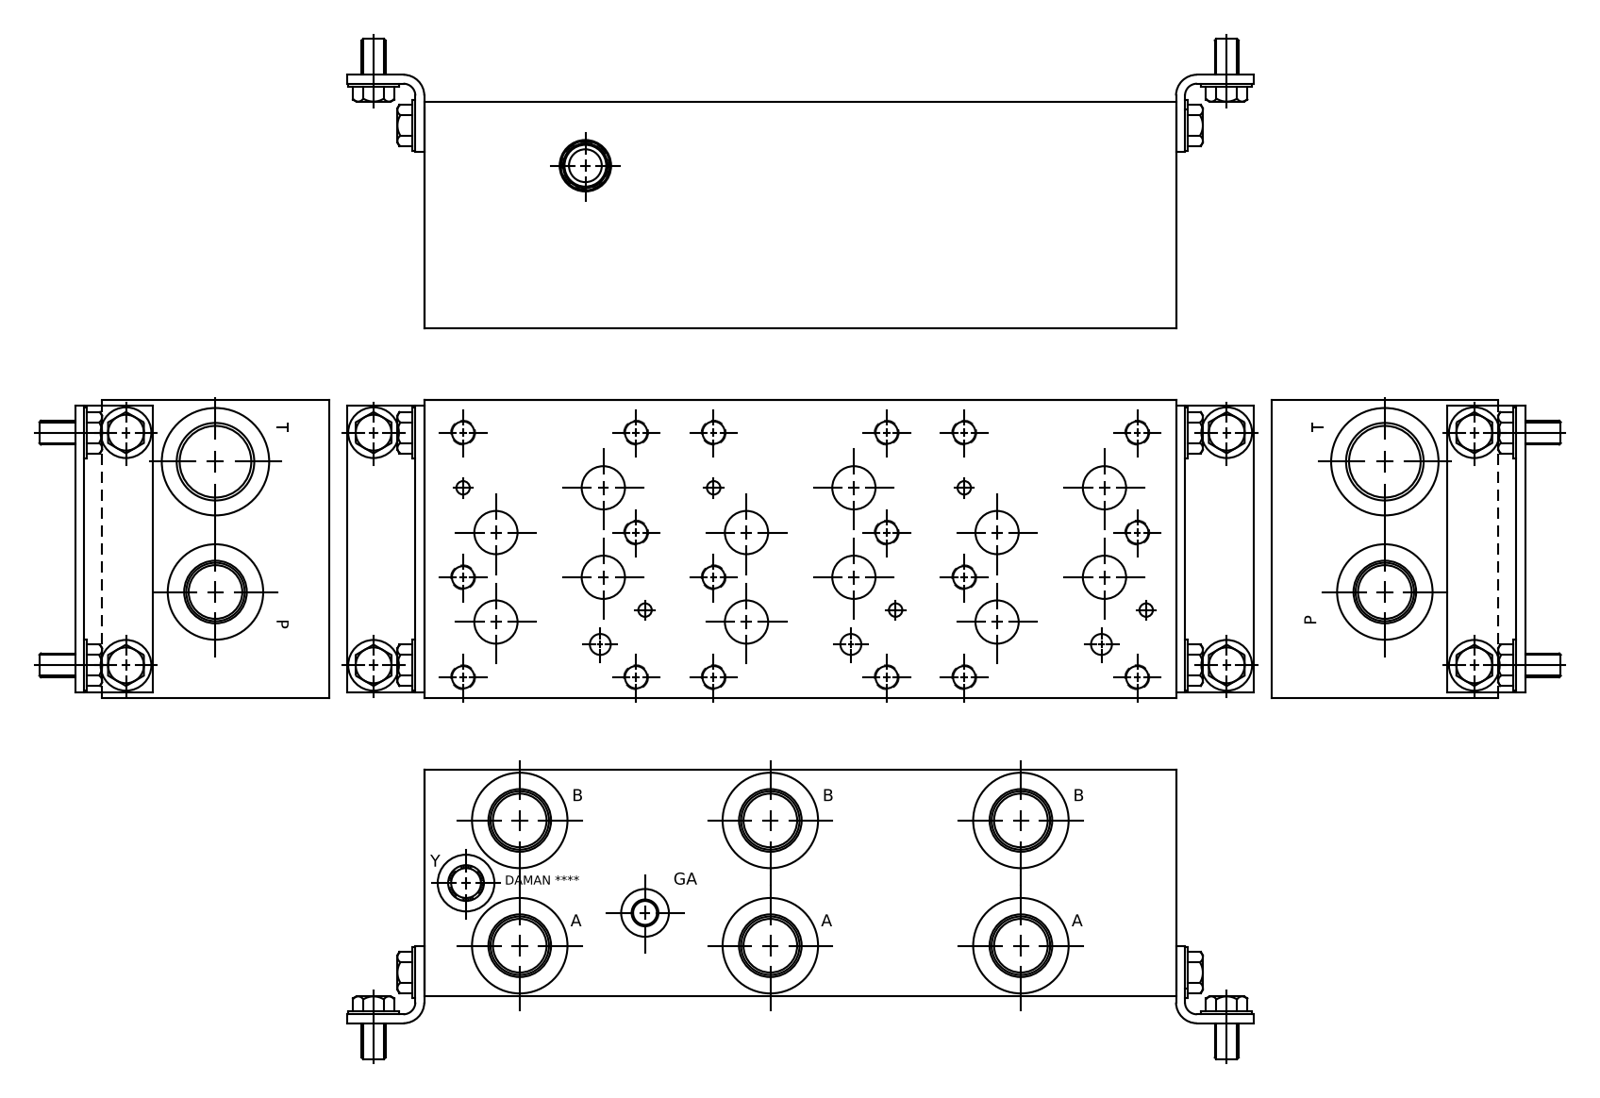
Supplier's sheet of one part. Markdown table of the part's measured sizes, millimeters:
| quantity | value |
| --- | --- |
| part name | Part_AD08P035S~S_3D |
| STEP written by | Autodesk Inventor 2021 (AUTOMOTIVE_DESIGN) |
| units | millimeters |
| bodies | 1 solid, 863 faces (416 planar, 138 cylindrical, 309 other) |
| overall size | 400.05 × 158.75 × 120.65 |
| volume | 7 141 000 mm³ |
| surface area | 345 693 mm² |
| round holes (diameter × count) | 10.72 × 21, 12.7 × 20, 23.01 × 11, 31.27 × 7, 33.76 × 7, 49.12 × 7, 7.14 × 6, 28.57 × 6, 33.35 × 6, 35.51 × 6, 11.13 × 2, 33.34 × 2 |
| main face-to-face distances | 120.65, 158.75, 400.05, 0.79, 157.96, 399.26, 398.47, 19.84, 19.05, 90.42 |
| hole center spacings | 133.35, 266.7, 61.92, 74.63, 118.29, 152.7, 191.98, 29.53 |
